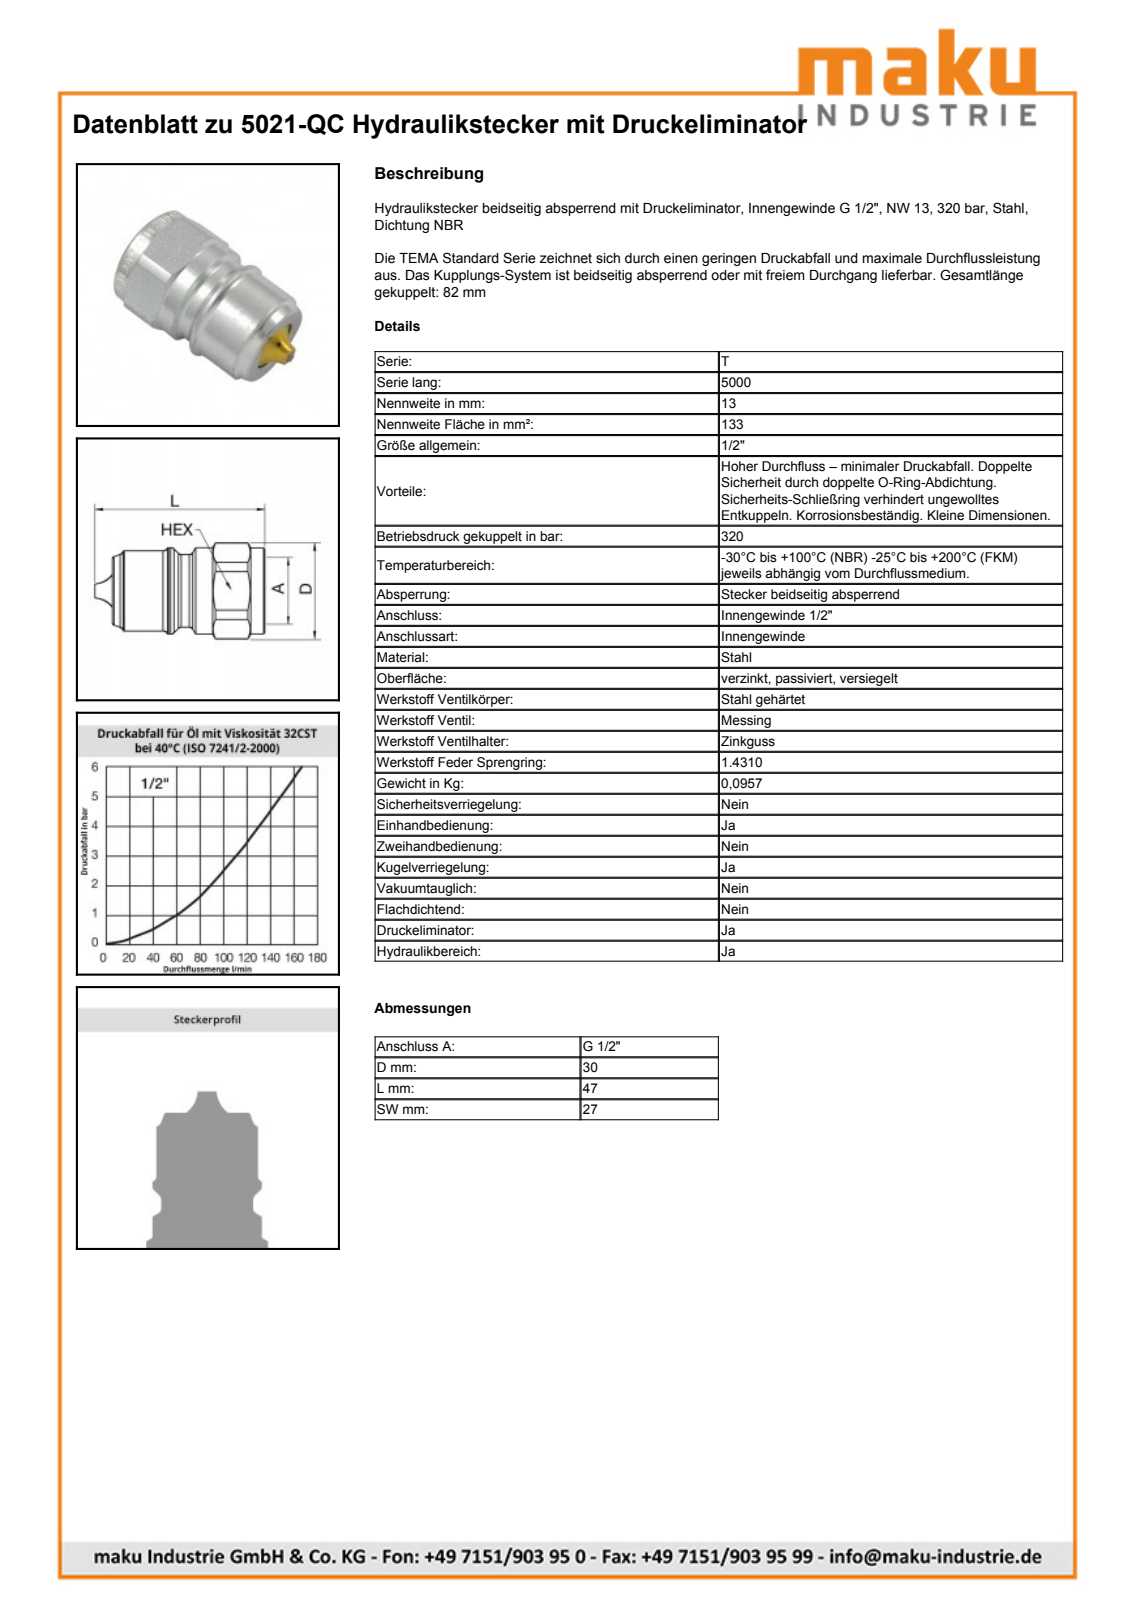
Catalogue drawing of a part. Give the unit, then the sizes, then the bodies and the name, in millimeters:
Units: millimetres
Overall size (bounding box): 46.19 × 29.3 × 27
Round holes (diameter × count): ⌀3.73 ×1, ⌀13 ×1, ⌀18.43 ×1
Round bosses / shafts (diameter × count): ⌀26.6 ×1, ⌀26.5 ×1, ⌀25.1 ×1, ⌀22.9 ×1
Partial cylindrical surfaces — rounded edges, fillets, slot ends (radius × count): R14.65 ×1
Main face-to-face distances: 27, 24.05, 41.5, 17.45, 4.25, 28.3, 45.75, 4.3, 28.35, 45.8
Volume: 17 272 mm³ · Surface area: 5 646 mm²
Bodies: 1 solid, 69 faces (13 planar, 22 cylindrical, 34 other)
Part name (STEP PRODUCT): 5021-QC
STEP written by: SolidWorks 2009 (AUTOMOTIVE_DESIGN)
